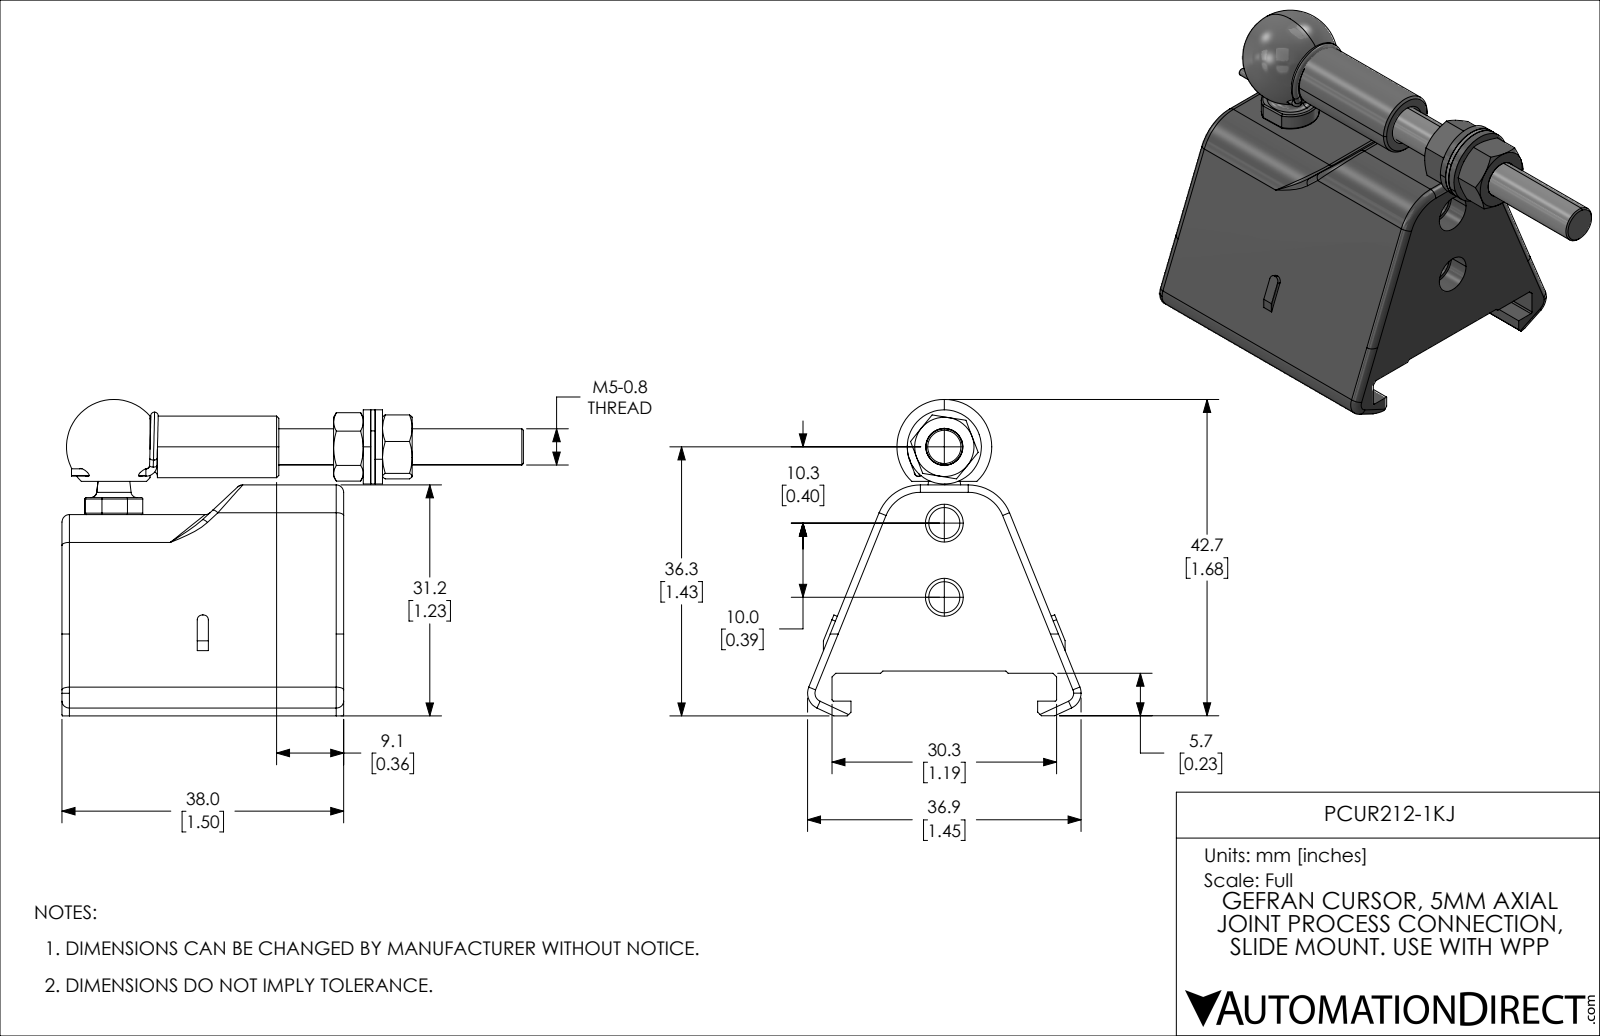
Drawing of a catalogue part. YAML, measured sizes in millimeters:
part_name: "PCUR212-1KJ"
step_written_by: "SolidWorks 2021 (CONFIG_CONTROL_DESIGN)"
units: millimeters
bodies: {solids: 11, faces: 378, planar: 107, cylindrical: 119, other: 152}
overall_size: [62.25, 42.68, 36.91]
volume: 24665
surface_area: 11148
round_holes:
  - {diameter: 4.2, count: 4}
  - {diameter: 5.1, count: 3}
  - {diameter: 1.1, count: 1}
  - {diameter: 5, count: 1}
  - {diameter: 5.3, count: 1}
round_bosses_or_shafts:
  - {diameter: 1, count: 2}
  - {diameter: 10, count: 1}
  - {diameter: 8.3, count: 1}
  - {diameter: 5, count: 1}
  - {diameter: 4.89, count: 1}
partial_cylinders:
  - {radius: 1, count: 14}
  - {radius: 0.45, count: 8}
  - {radius: 0.2, count: 6}
  - {radius: 0.7, count: 4}
  - {radius: 6, count: 4}
  - {radius: 2.2, count: 2}
  - {radius: 3.9, count: 1}
face_to_face_distances: [38, 12, 13, 25, 9.15, 21.15, 2, 5.75, 1, 6.6]
hole_center_spacings: [4.91, 7.67, 10, 10.28, 17.19, 20.28]
